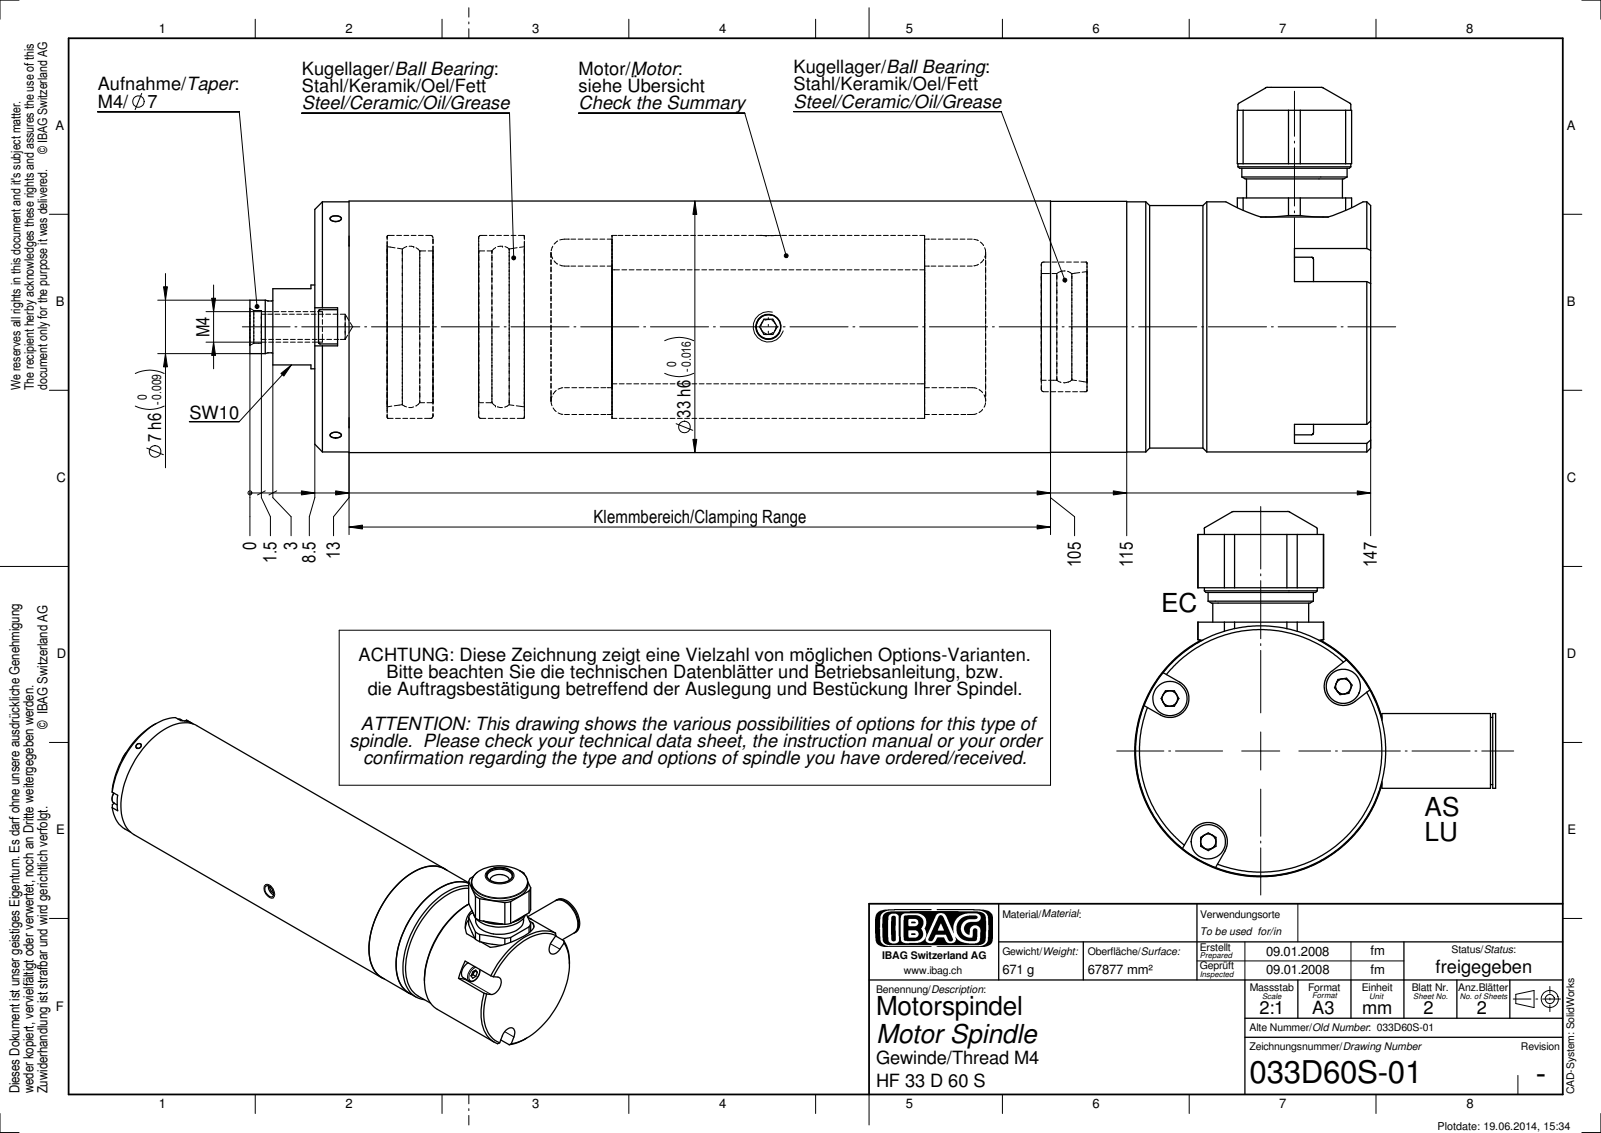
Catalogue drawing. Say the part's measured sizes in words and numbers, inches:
The part is named "033D60S-01". Its 3-D file was written by "SolidWorks 2014 (CONFIG_CONTROL_DESIGN)". It is 0 solids with 252 faces: 108 planar, 86 cylindrical and 58 other. Overall it measures 5.787 by 1.886 by 1.862 inches. Round holes: 2 of diameter 0.13, 1 of diameter 0.169, 1 of diameter 0.197, 1 of diameter 0.236, 1 of diameter 0.264, 1 of diameter 0.449. Round bosses or shafts: 6 of diameter 0.177, 1 of diameter 1.299, 1 of diameter 1.295, 1 of diameter 1.291, 1 of diameter 1.252, 1 of diameter 0.583, 1 of diameter 0.543, 1 of diameter 0.496. Partial cylindrical surfaces (rounded edges, fillets, slot ends): 6 of radius 0.098, 1 of radius 0.207, 1 of radius 0.325, 1 of radius 0.354. The main face-to-face distances are 5.453, 1.26, 0.394, 4.193, 4.016, 5.276, 0.177, 3.799, 1.654, 3.622. The hole center spacings are 2.48.
